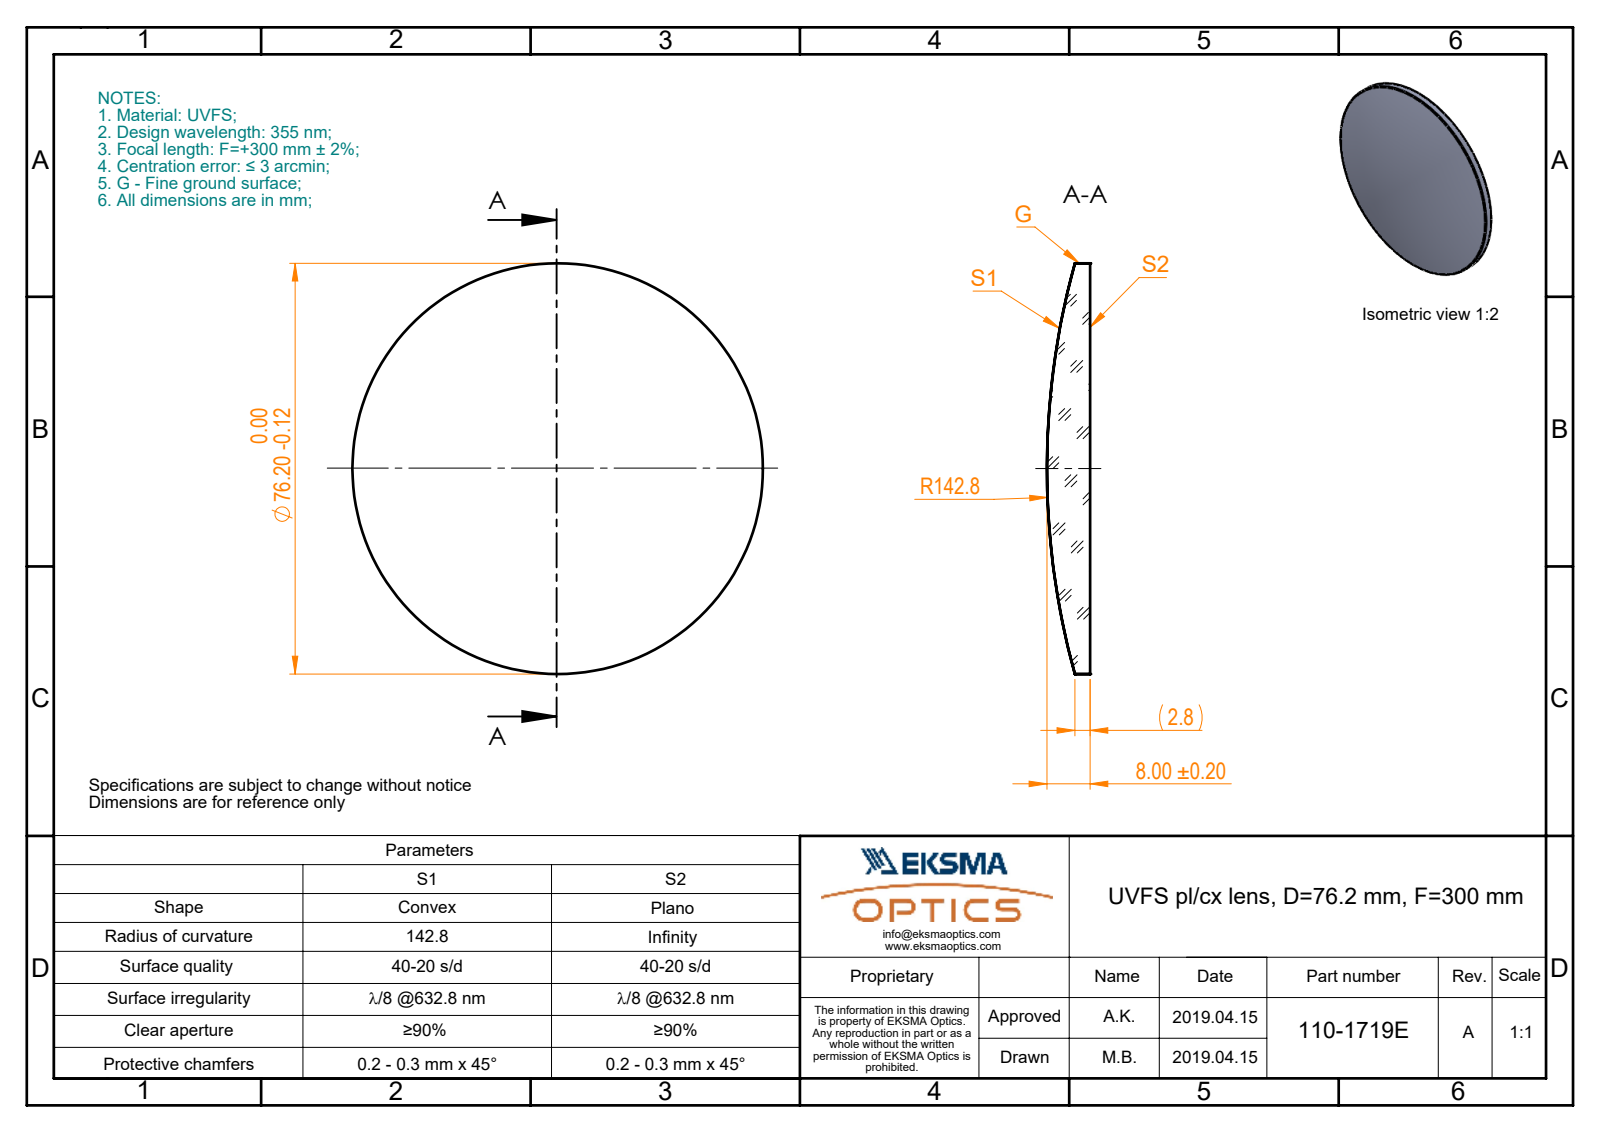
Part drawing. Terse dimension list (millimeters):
name: 110-1719E UVFS pl-cx 76.2 F300
written by: SolidWorks 2017 (CONFIG_CONTROL_DESIGN)
unit: mm
bodies: 1 solid, 5 faces (1 planar, 2 cylindrical, 2 other)
size: 76.2 × 76.2 × 8
volume: 24 752 mm³; area: 9 881 mm²
bosses: 1× ⌀76.2
